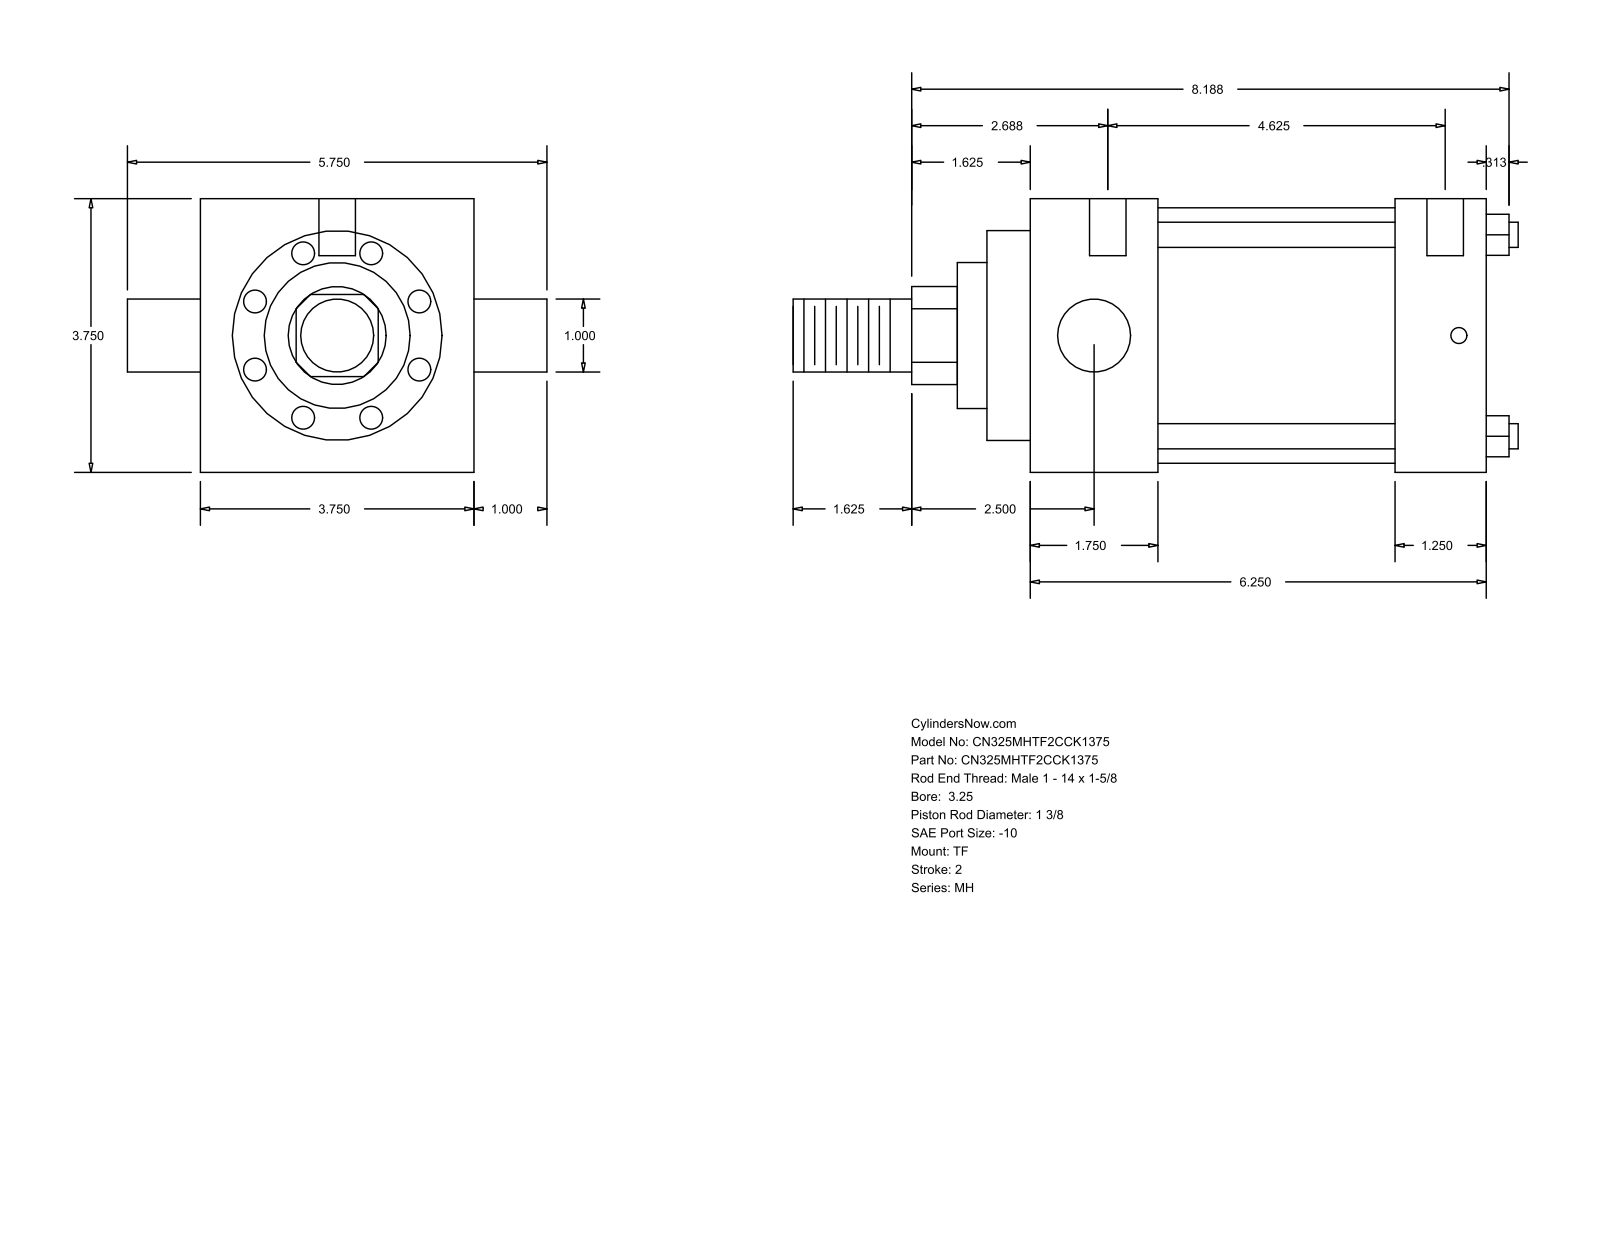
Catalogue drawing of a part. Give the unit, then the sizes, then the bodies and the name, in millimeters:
Units: millimetres
Overall size (bounding box): 252.41 × 146.05 × 95.25
Round holes (diameter × count): ⌀5.56 ×3, ⌀12.7 ×2
Round bosses / shafts (diameter × count): ⌀8.76 ×4, ⌀25.4 ×2, ⌀88.9 ×1, ⌀73.03 ×1, ⌀50.8 ×1, ⌀34.92 ×1
Partial cylindrical surfaces — rounded edges, fillets, slot ends (radius × count): R17.06 ×1
Main face-to-face distances: 95.24, 158.76, 44.45, 127.01, 82.56, 114.31, 31.75, 15.08, 59.53, 142.09
Hole centre spacings: 1.59, 4.76, 117.48, 119.07, 122.24, 123.83
Bodies: 0 solids, 86 faces (61 planar, 25 cylindrical, 0 other)
Part name (STEP PRODUCT): MH_TF__0325_1.375
STEP written by: GSSL Pune (CONFIG_CONTROL_DESIGN)
